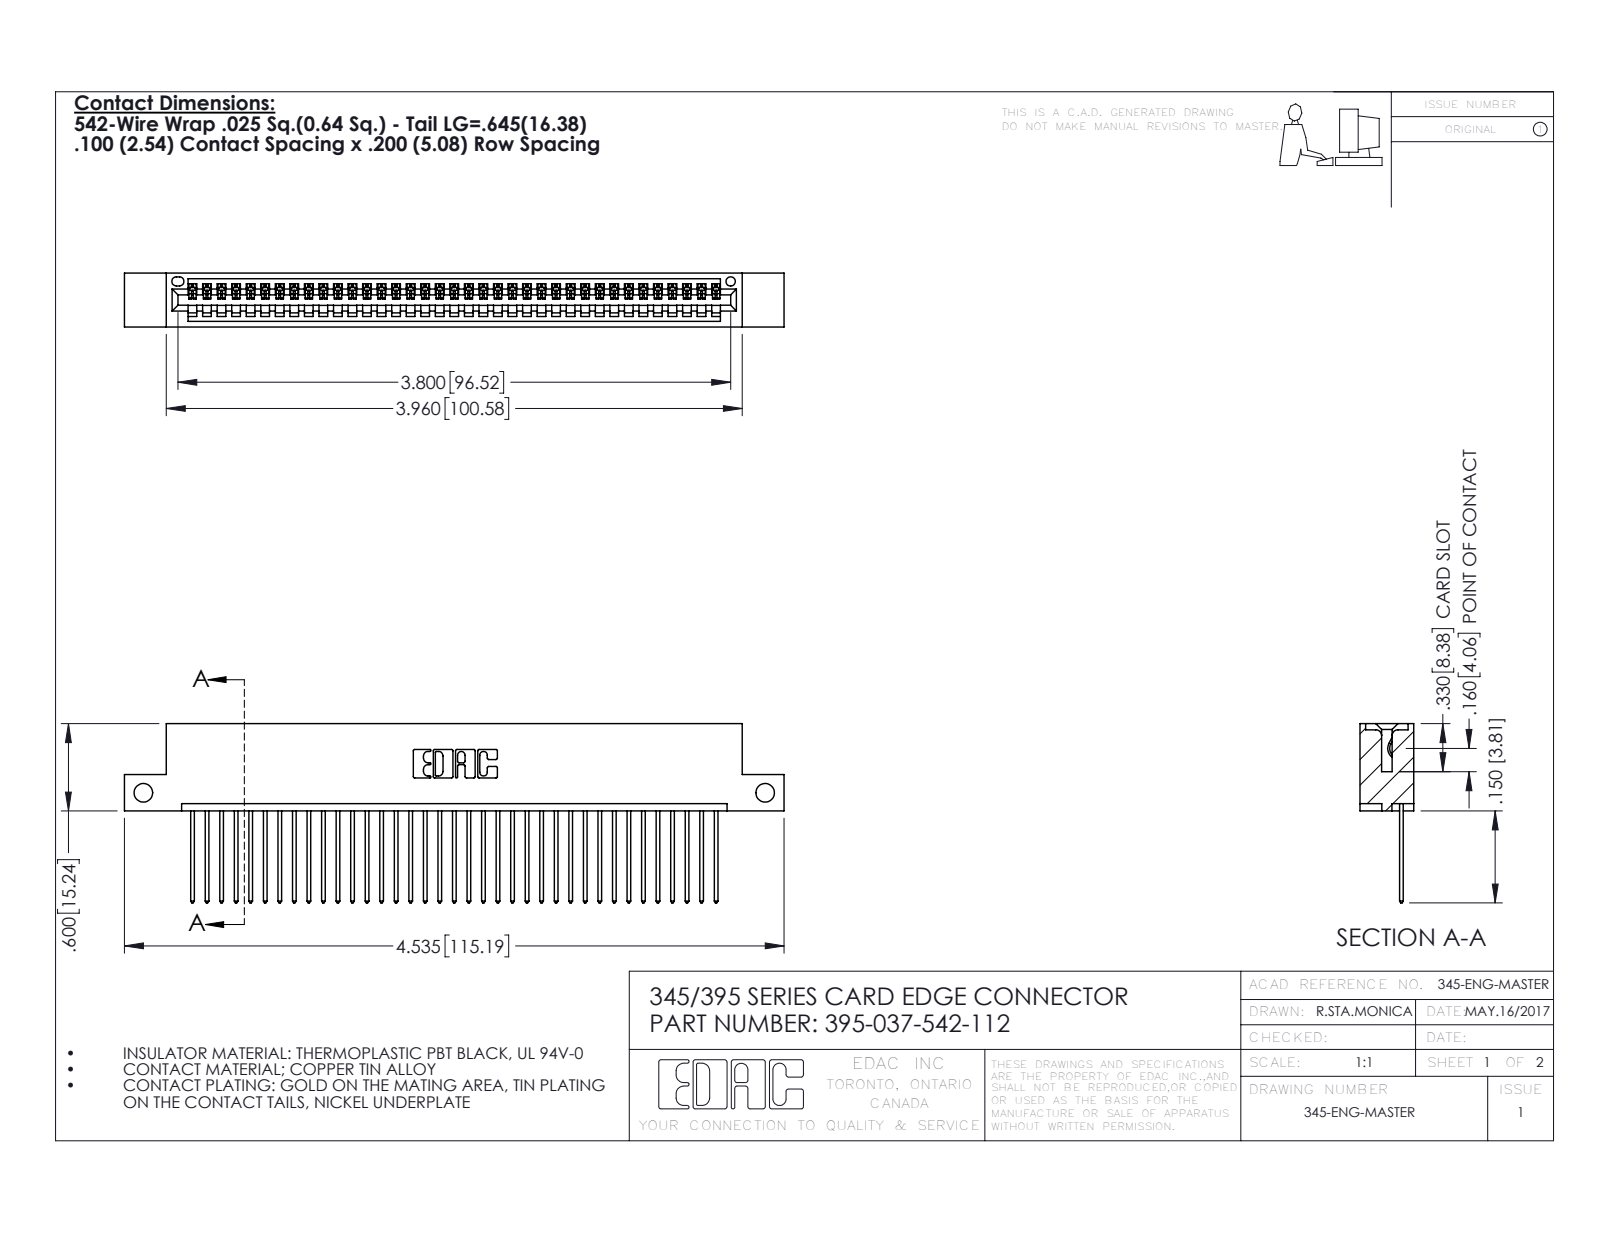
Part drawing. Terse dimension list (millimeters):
name: 395-037-542-112; 345 Part_Flush Mounting Lugs - Side Mount; 345-292-001_345-293-142
written by: SolidWorks 2016 (CONFIG_CONTROL_DESIGN)
unit: mm
bodies: 38 solids, 2272 faces (1560 planar, 712 cylindrical, 0 other)
size: 115.2 × 31.3 × 9.4
volume: 10 900 mm³; area: 14 790 mm²
holes: 2× ⌀3.3, 1× ⌀1.6
rounds: 74× R0.2, 74× R0.3, 22× R0.3, 6× R0.2, 6× R0.8, 3× R0.7, 2× R0.8, 2× R1
face distances: 1.8, 7.6, 5.1, 9.4, 2.5, 6.9, 0.6, 5.7, 3.8, 1.8
hole spacings: 108.6
